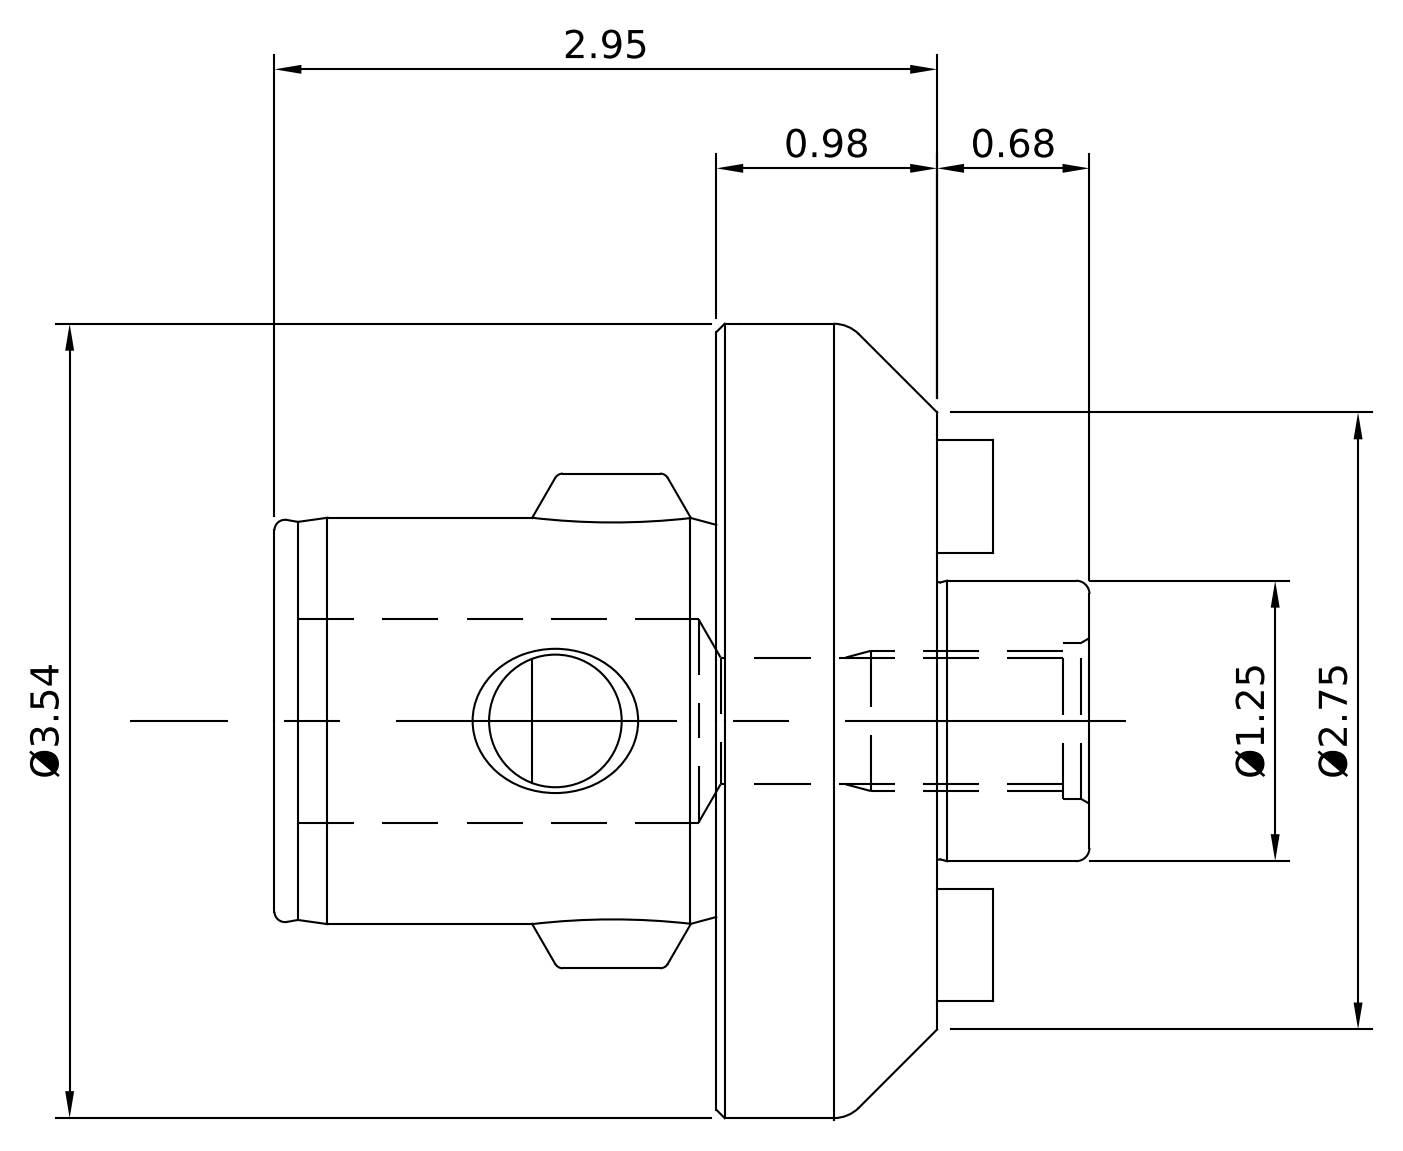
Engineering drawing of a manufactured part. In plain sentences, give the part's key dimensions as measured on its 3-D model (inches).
The part is named "11.690.712; 11.691.623; 691-50XRing_10.691.507Ring; 10.691.50X_10.691.507 (+1 more)". Its 3-D file was written by "SolidWorks 2010 (CONFIG_CONTROL_DESIGN)". It is 6 solids with 264 faces: 56 planar, 79 cylindrical and 129 other. Overall it measures 4.203 by 3.543 by 3.543 inches. Its volume is 14.57 cubic inches and its surface area 70.37 square inches. Round holes: 2 of diameter 0.5, 1 of diameter 0.316, 1 of diameter 0.578, 1 of diameter 0.591, 1 of diameter 0.693, 1 of diameter 0.709, 1 of diameter 0.866, 1 of diameter 0.972. Round bosses or shafts: 1 of diameter 3.543, 1 of diameter 1.811, 1 of diameter 1.5, 1 of diameter 1.25, 1 of diameter 0.705, 1 of diameter 0.626, 1 of diameter 0.625, 1 of diameter 0.472. Partial cylindrical surfaces (rounded edges, fillets, slot ends): 1 of radius 0.906. The main face-to-face distances are 0.984, 0.5, 2.234, 1.25, 1.969, 2.953, 4.203, 3.703, 1.734, 0.75. The hole center spacings are 1, 2.
